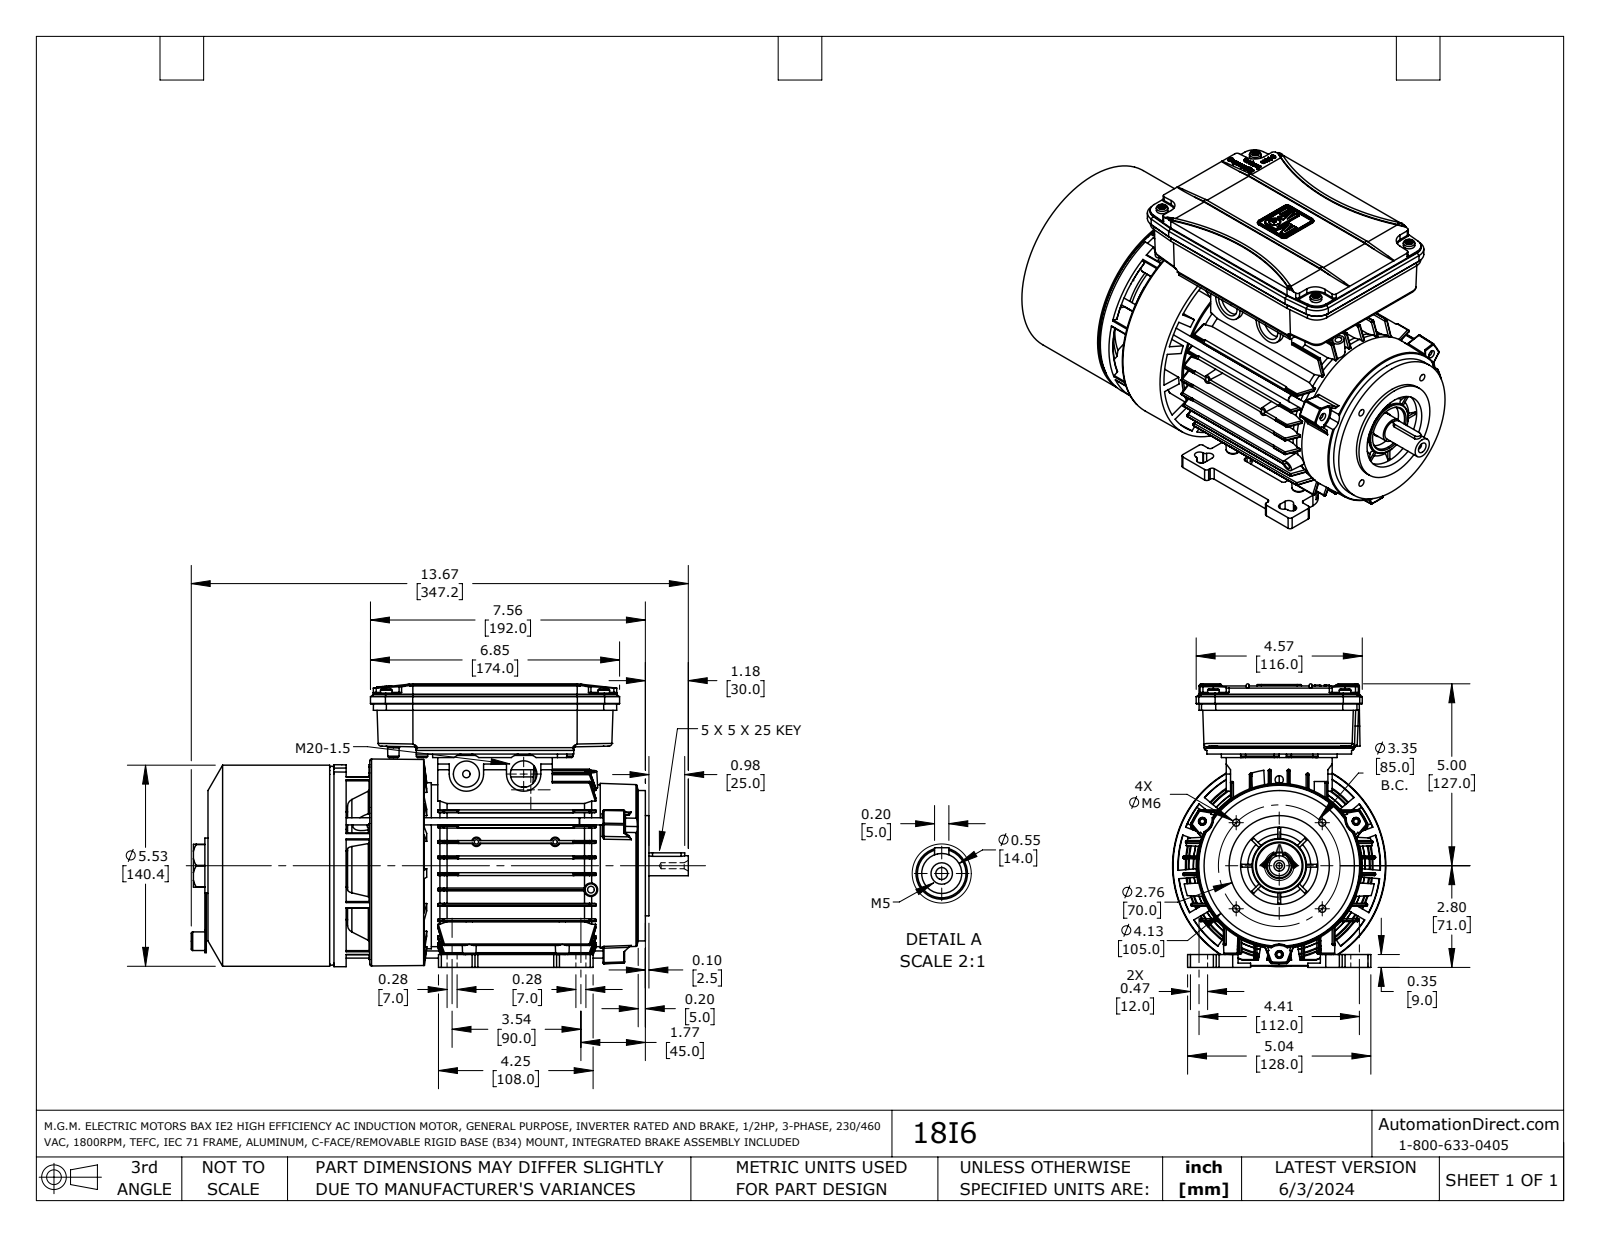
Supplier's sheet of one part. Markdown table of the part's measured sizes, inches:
| quantity | value |
| --- | --- |
| part name | 18I6 |
| STEP written by | SolidWorks 2021 (AUTOMOTIVE_DESIGN) |
| units | inches |
| bodies | 28 solids, 4175 faces (1389 planar, 1316 cylindrical, 1470 other) |
| overall size | 13.668 × 7.795 × 5.866 |
| volume | 67.73 in³ |
| surface area | 1 097 in² |
| round holes (diameter × count) | 0.13 × 21, 0.177 × 12, 0.236 × 11, 0.217 × 10, 0.157 × 8, 0.098 × 7, 0.118 × 6, 0.197 × 4, 0.256 × 4, 0.394 × 4, 0.276 × 3, 0.185 × 2 |
| round bosses / shafts (diameter × count) | 0.177 × 8, 0.118 × 8, 0.197 × 7, 0.386 × 4, 0.315 × 4, 5.551 × 1, 5.528 × 1, 5.425 × 1 |
| partial cylindrical surfaces (radius × count) | 0.079 × 63, 0.035 × 60, 0.008 × 56, 0.02 × 56, 0.039 × 48, 0.024 × 28, 0.012 × 24, 0.004 × 16 |
| main face-to-face distances | 0.079, 0.422, 0.843, 1.726, 0.354, 2.57, 0.343, 2.148, 0.5, 1.805 |
| hole center spacings | 0.472, 0.818, 2.018, 2.486, 2.86, 4.204, 3.272, 0.743 |
